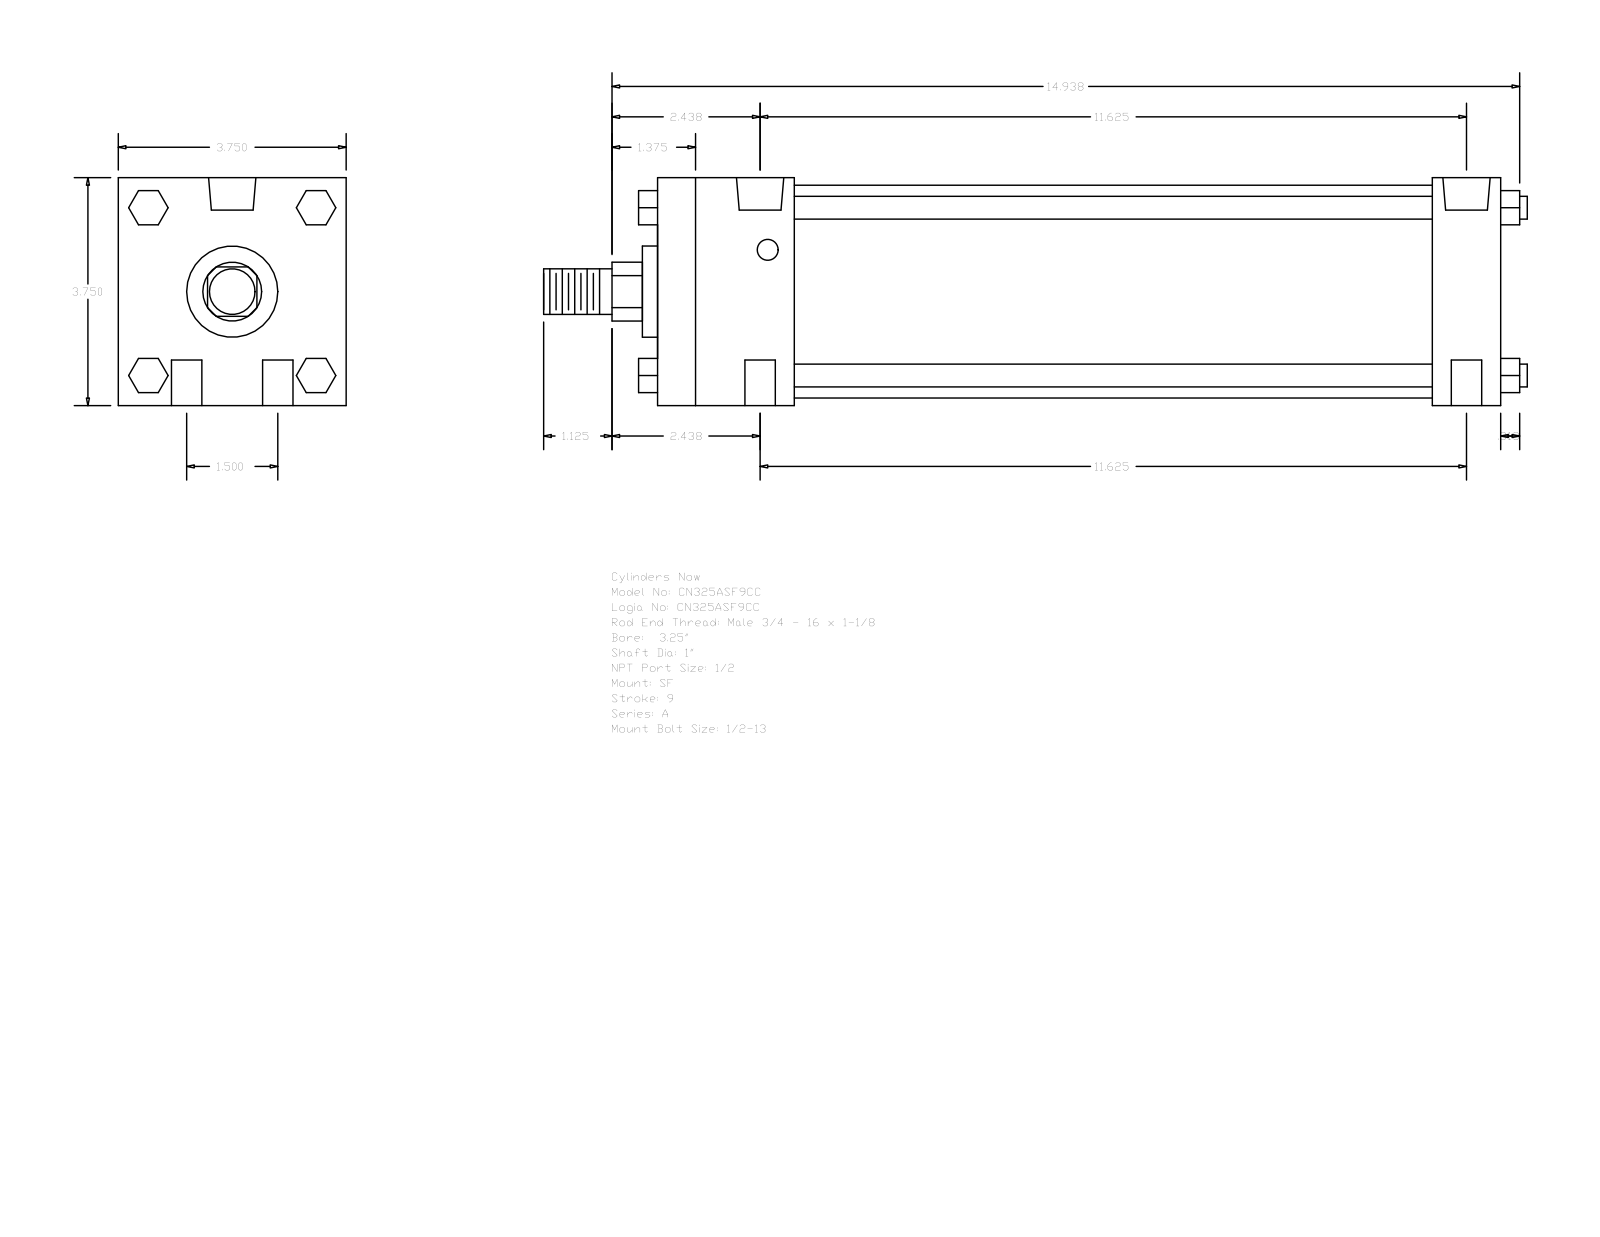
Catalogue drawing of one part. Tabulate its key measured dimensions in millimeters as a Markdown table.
| quantity | value |
| --- | --- |
| part name | A_SF__0325_1 |
| STEP written by | GSSL Pune (CONFIG_CONTROL_DESIGN) |
| units | millimeters |
| bodies | 0 solids, 124 faces (94 planar, 30 cylindrical, 0 other) |
| overall size | 411.16 × 95.25 × 95.25 |
| round holes (diameter × count) | 12.7 × 4, 8.73 × 2, 19.77 × 2 |
| round bosses / shafts (diameter × count) | 9.53 × 4, 88.9 × 1, 38.1 × 1, 25.4 × 1, 19.05 × 1 |
| partial cylindrical surfaces (radius × count) | 12.29 × 1 |
| main face-to-face distances | 95.24, 352.43, 323.85, 28.58, 57.15, 266.7, 295.28, 14.28, 35.05, 60.71 |
| hole center spacings | 19.05, 295.89, 295.28, 38.1, 297.73, 288.92 |
